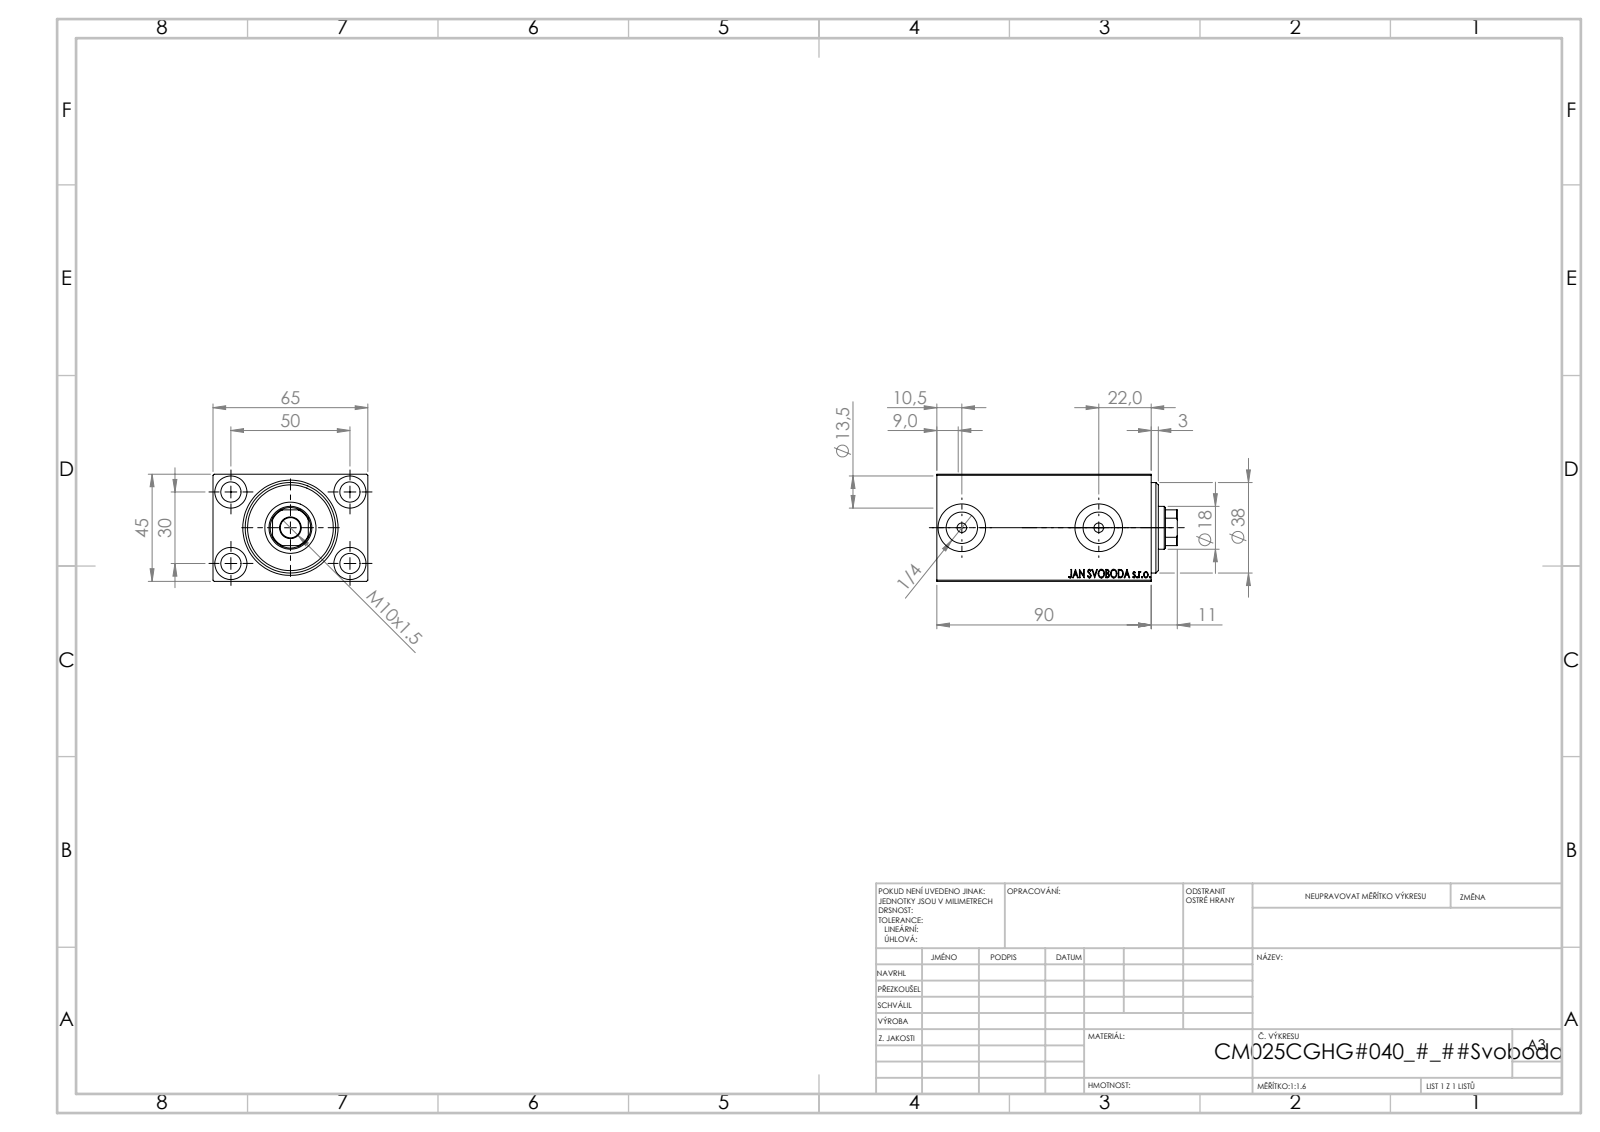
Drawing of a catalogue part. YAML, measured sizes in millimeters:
part_name: "V450CM_C_VCP; V450CM_C_Body; V450CM_VC_B"
step_written_by: "SolidWorks 2019 (CONFIG_CONTROL_DESIGN)"
units: millimeters
bodies: {solids: 3, faces: 862, planar: 408, cylindrical: 60, other: 394}
overall_size: [101, 65, 45]
volume: 227331
surface_area: 55364
round_holes:
  - {diameter: 8.5, count: 5}
  - {diameter: 13.5, count: 4}
  - {diameter: 4, count: 2}
  - {diameter: 13.16, count: 2}
  - {diameter: 20, count: 2}
  - {diameter: 18, count: 1}
  - {diameter: 21.5, count: 1}
  - {diameter: 25, count: 1}
  - {diameter: 27, count: 1}
  - {diameter: 38, count: 1}
partial_cylinders:
  - {radius: 8.5, count: 1}
face_to_face_distances: [45, 65, 6, 79, 84, 85, 5, 90, 3, 8]
hole_center_spacings: [29.15, 30, 50, 58.31, 57.5]
